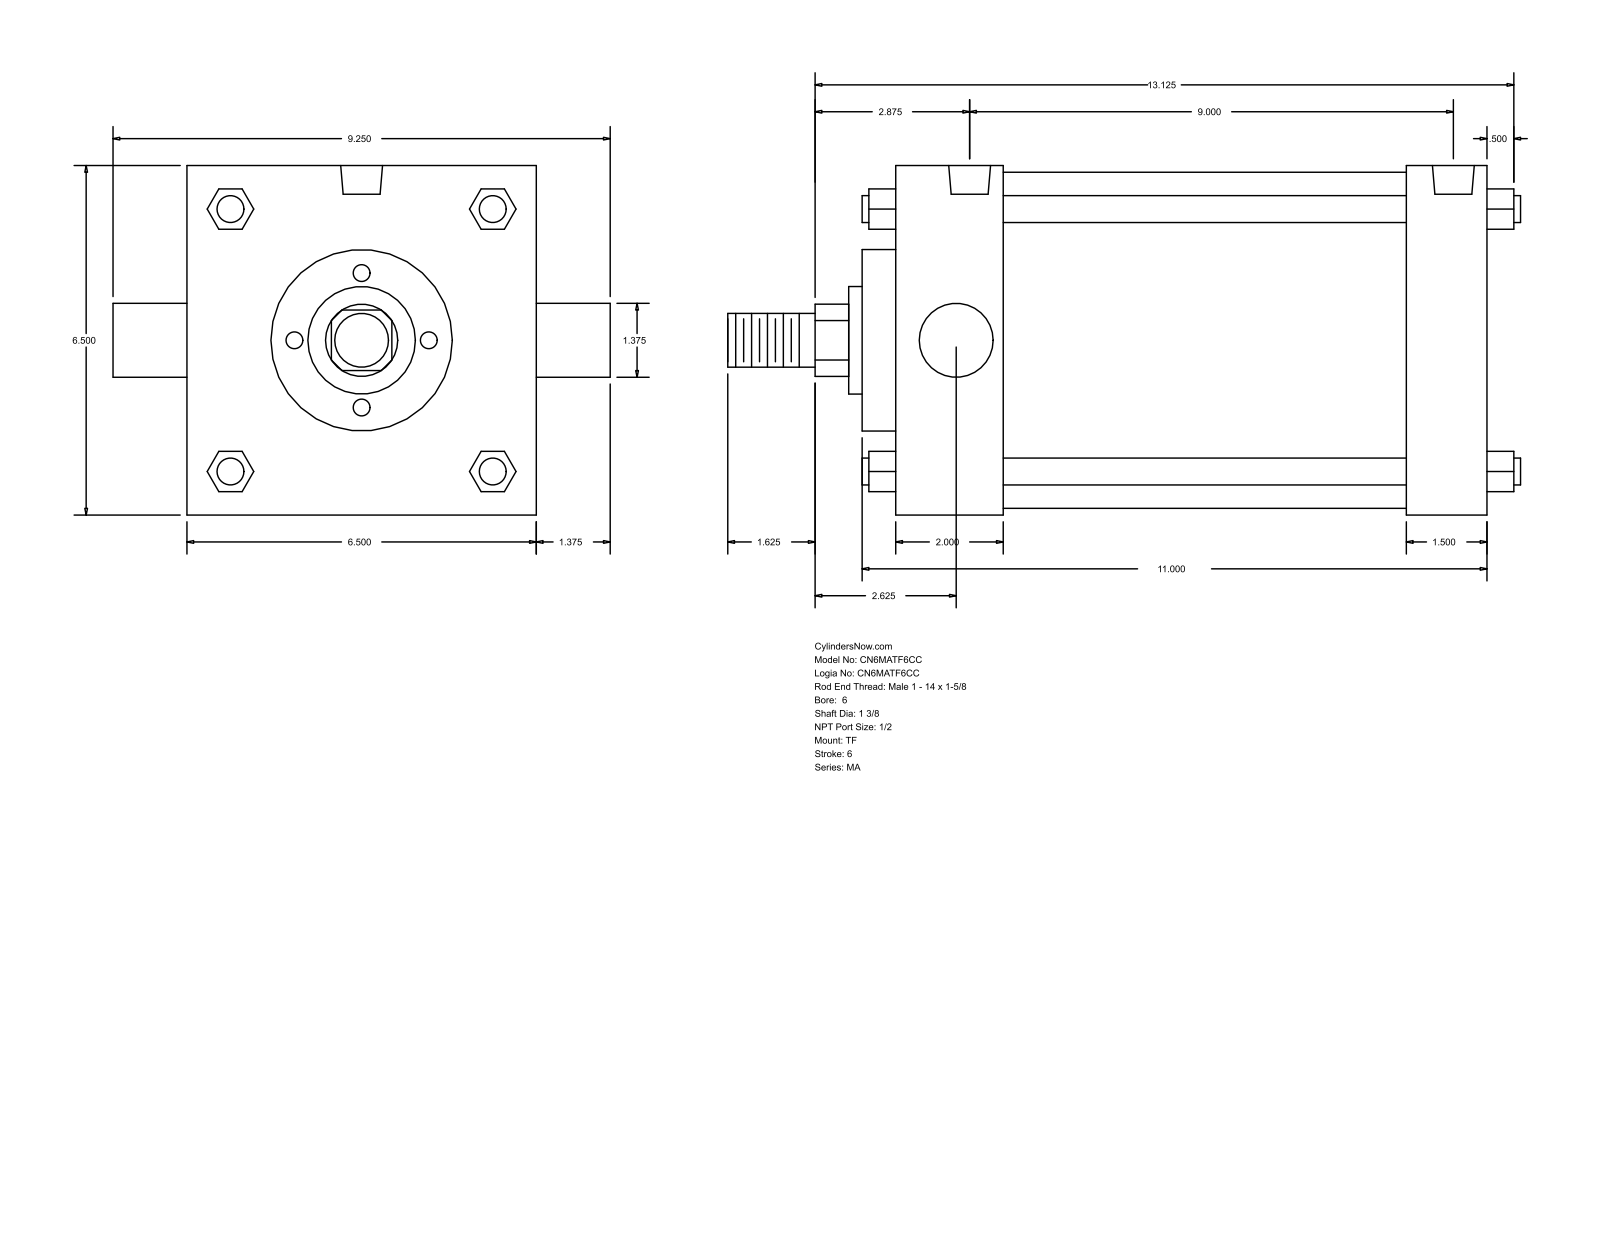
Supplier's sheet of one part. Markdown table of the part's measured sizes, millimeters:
| quantity | value |
| --- | --- |
| part name | MA_TF__0600_1.375 |
| STEP written by | GSSL Pune (CONFIG_CONTROL_DESIGN) |
| units | millimeters |
| bodies | 0 solids, 122 faces (93 planar, 29 cylindrical, 0 other) |
| overall size | 374.65 × 234.95 × 165.1 |
| round holes (diameter × count) | 17.46 × 3, 19.77 × 2 |
| round bosses / shafts (diameter × count) | 12.7 × 4, 34.92 × 2, 158.75 × 1, 85.72 × 1, 50.8 × 1, 25.4 × 1 |
| partial cylindrical surfaces (radius × count) | 17.06 × 1 |
| main face-to-face distances | 165.1, 282.58, 50.8, 231.78, 244.47, 193.67, 38.11, 66.67, 15.87, 260.34 |
| hole center spacings | 3.18, 228.59, 231.77 |
